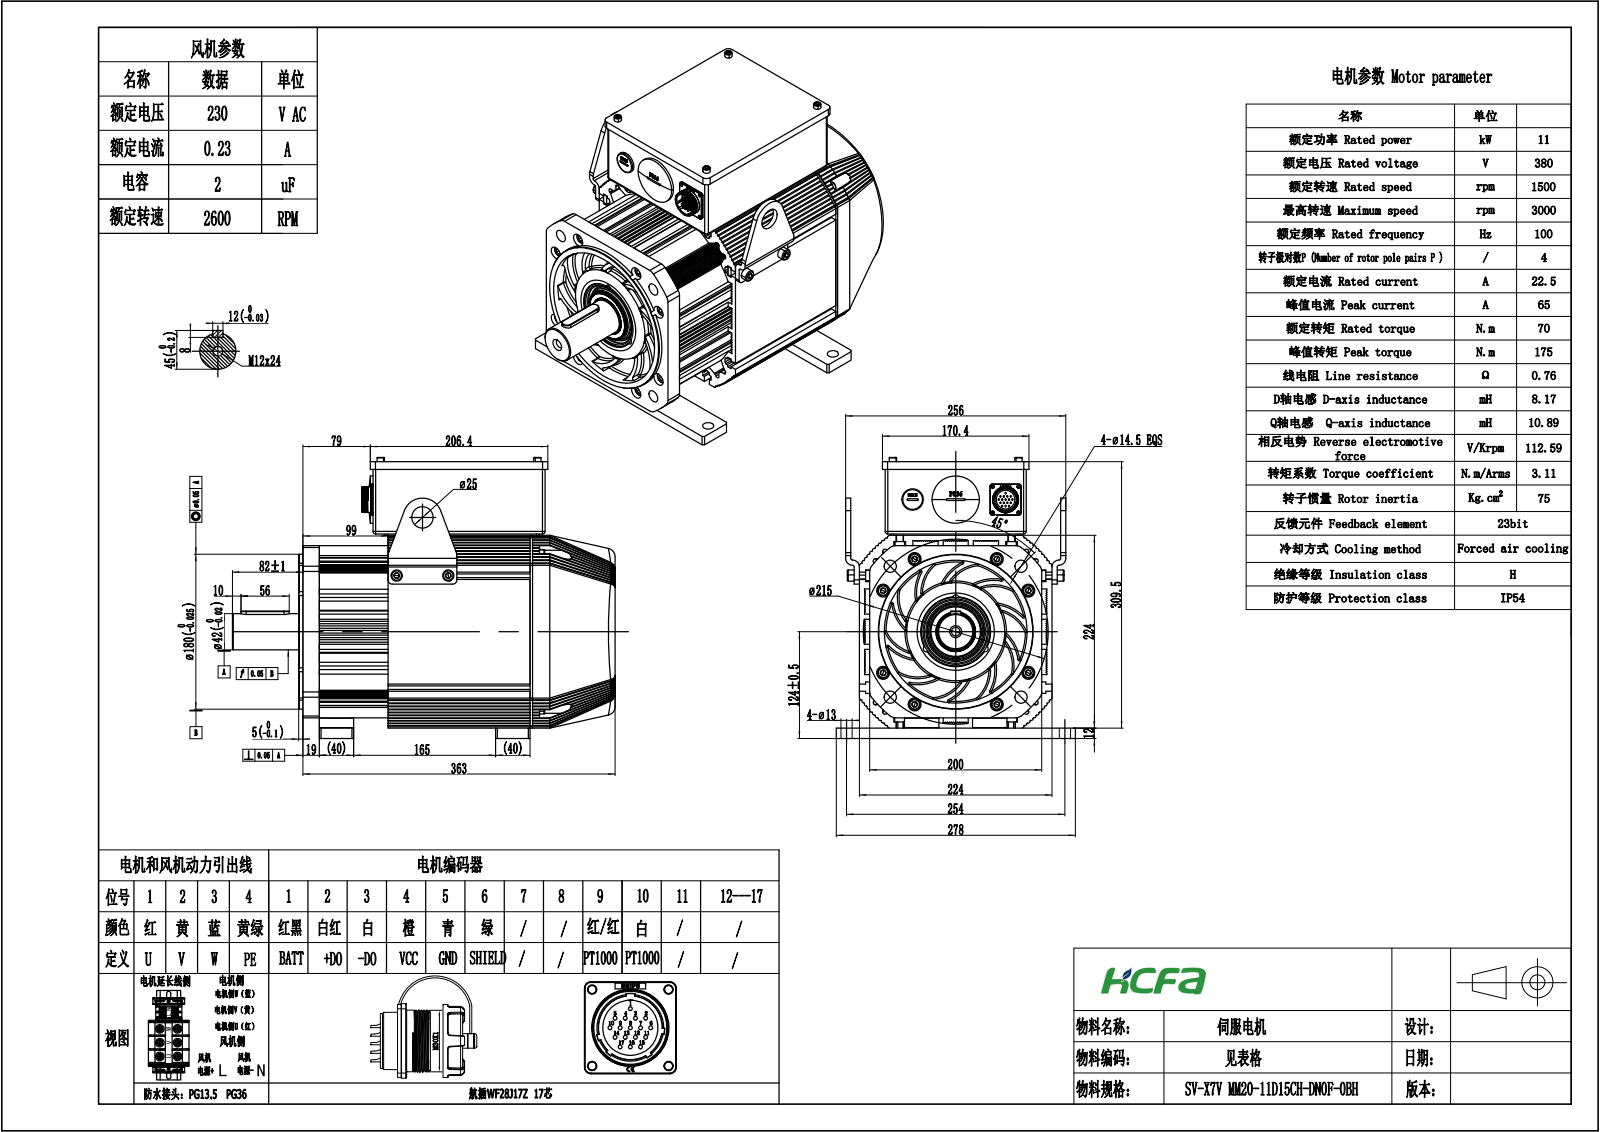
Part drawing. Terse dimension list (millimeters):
name: 10002030101-0031-SV-X7VMM20-11D15CH-DN0F-0BH-3段外形图
written by: SolidWorks 2021 (CONFIG_CONTROL_DESIGN)
unit: mm
bodies: 20 solids, 3500 faces (1518 planar, 975 cylindrical, 1007 other)
size: 445 × 326.5 × 278
volume: 15 120 000 mm³; area: 1 057 000 mm²
holes: 22× ⌀9, 14× ⌀15, 12× ⌀6.8, 9× ⌀5, 4× ⌀2.5, 4× ⌀7, 4× ⌀10, 4× ⌀13, 4× ⌀14.5, 1× ⌀10.2, 1× ⌀20.5, 1× ⌀21.7
bosses: 20× ⌀8, 17× ⌀1.5, 16× ⌀13, 4× ⌀10, 4× ⌀8.5, 4× ⌀7, 4× ⌀6.3, 4× ⌀6
rounds: 96× R2, 22× R1, 20× R1.5, 18× R5, 16× R1.4, 16× R3, 10× R0.2, 10× R10
face distances: 2, 12, 6, 4, 224, 307.5, 305.5, 309.5, 30, 194
hole spacings: 29.47, 43.17, 97, 124.07, 137.18, 138.41, 162.9, 167.15
